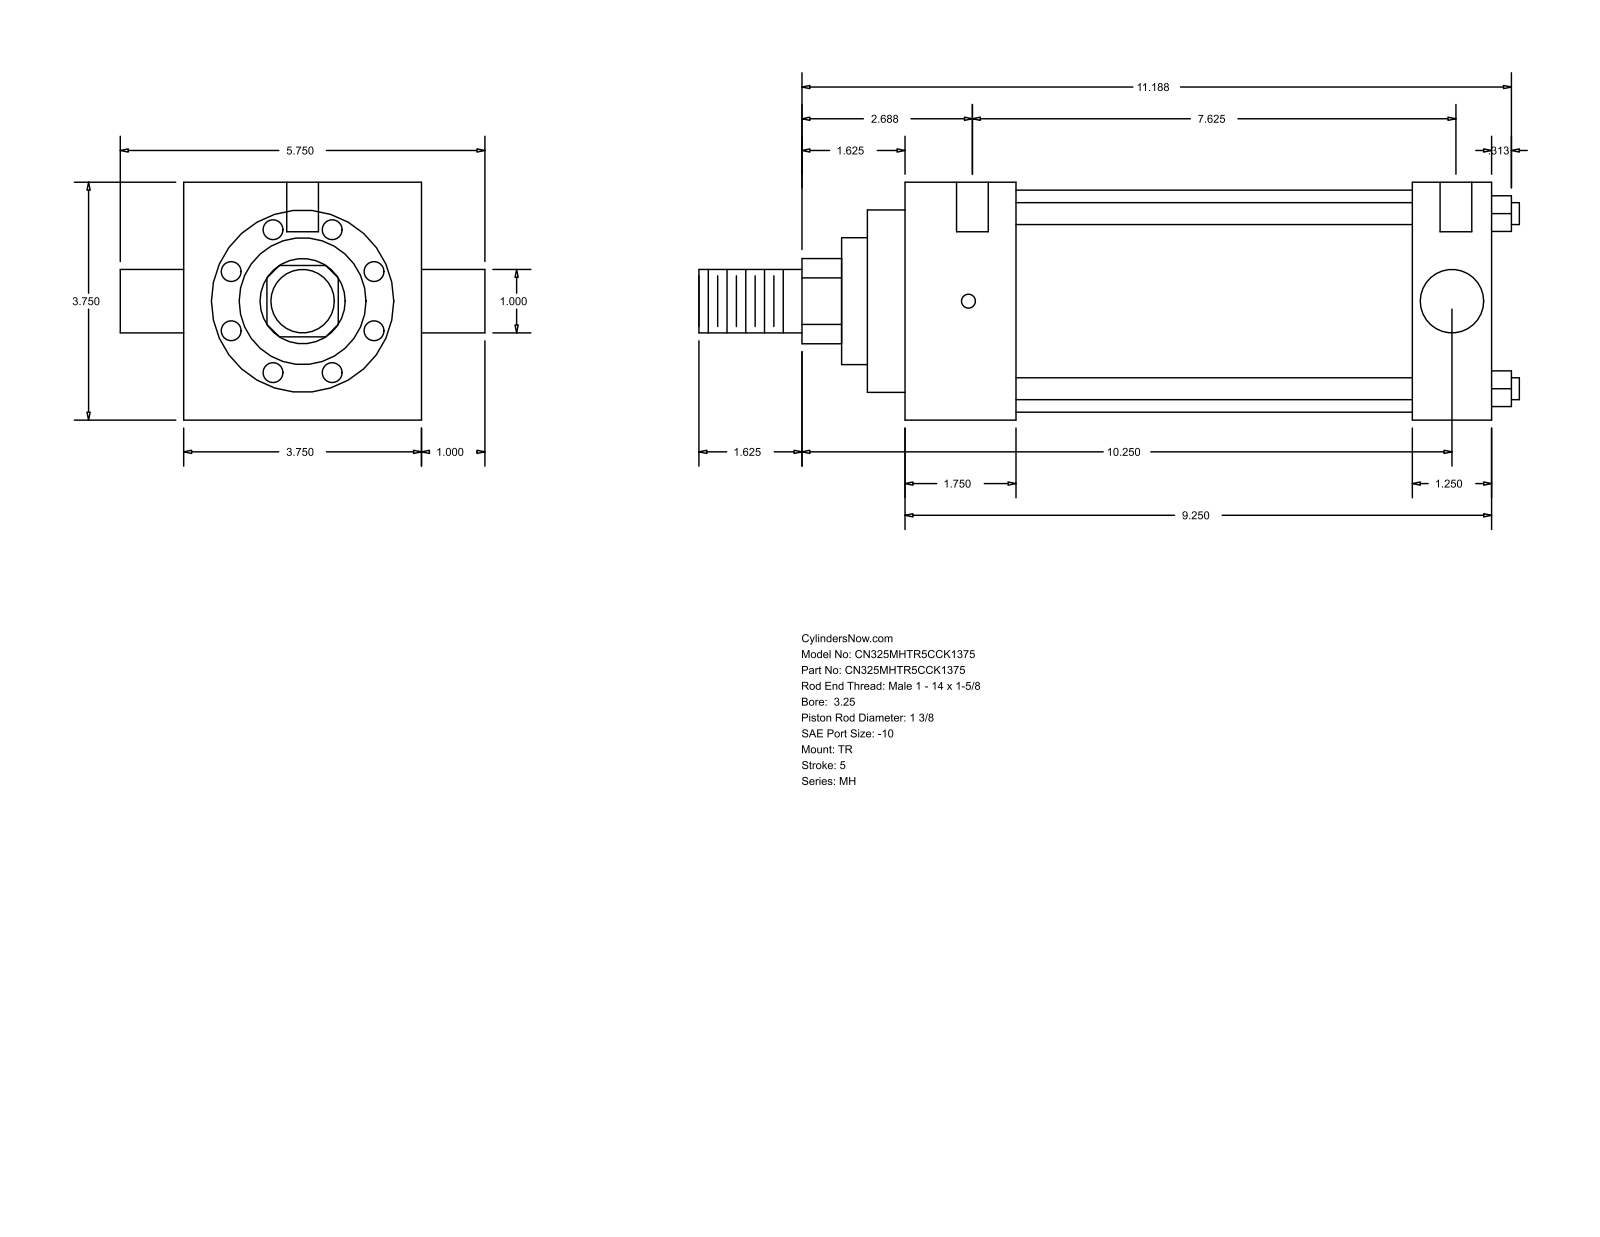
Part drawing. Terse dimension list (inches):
name: MH_TR__0325_1.375
written by: GSSL Pune (CONFIG_CONTROL_DESIGN)
unit: in
bodies: 0 solids, 86 faces (61 planar, 25 cylindrical, 0 other)
size: 12.937 × 5.75 × 3.75
holes: 3× ⌀0.219, 2× ⌀0.5
bosses: 4× ⌀0.345, 2× ⌀1, 1× ⌀3.5, 1× ⌀2.875, 1× ⌀2, 1× ⌀1.375
rounds: 1× R0.672
face distances: 3.75, 9.25, 1.75, 8, 6.25, 7.5, 1.25, 0.594, 2.344, 8.594
hole spacings: 0.063, 0.187, 7.625, 7.688, 7.813, 7.875
